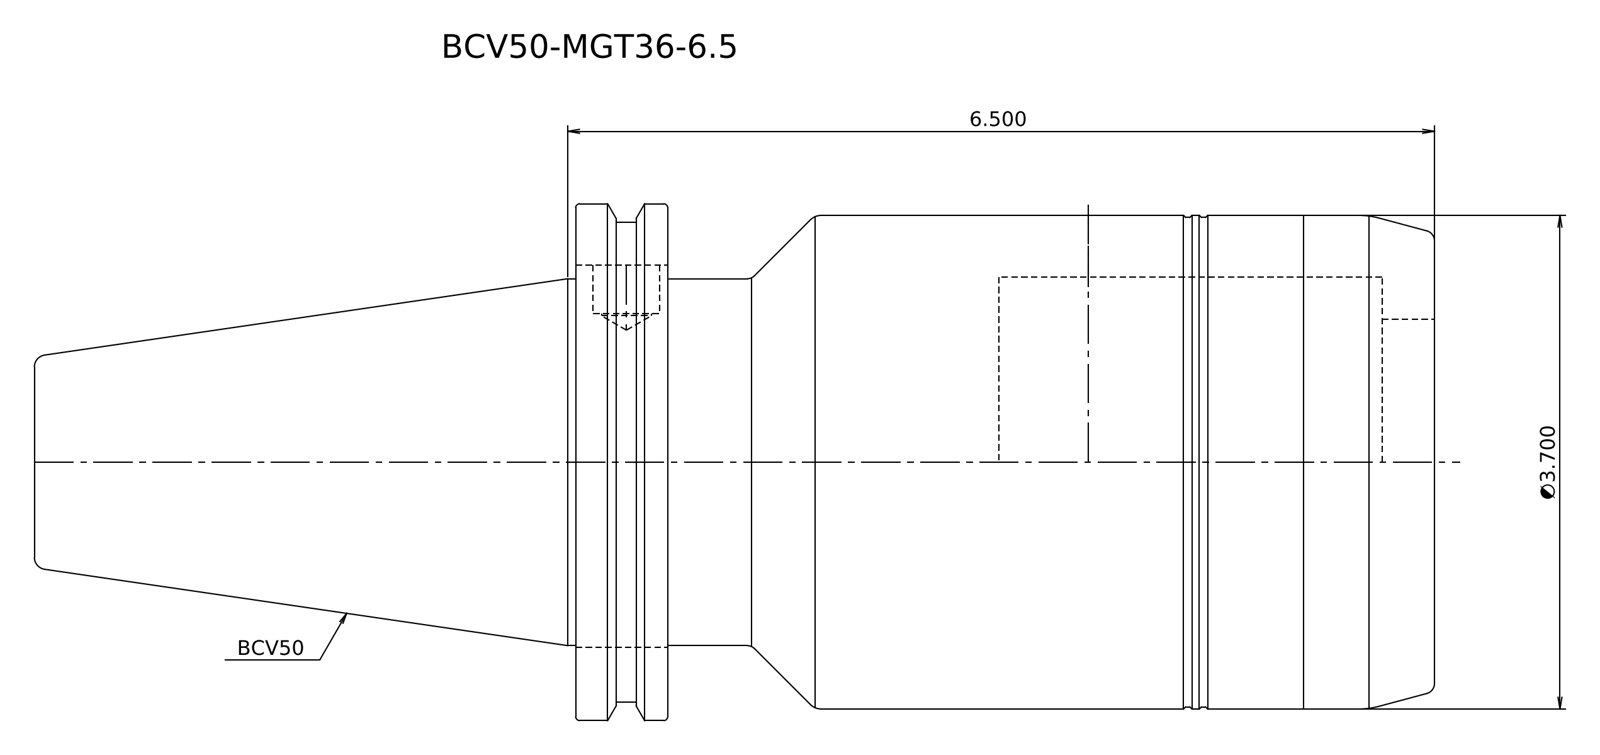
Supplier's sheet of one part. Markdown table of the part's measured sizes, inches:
| quantity | value |
| --- | --- |
| part name | BCV50-MGT36-6.5 |
| STEP written by | SolidWorks 2016 (CONFIG_CONTROL_DESIGN) |
| units | inches |
| bodies | 1 solid, 119 faces (38 planar, 29 cylindrical, 52 other) |
| overall size | 10.502 × 3.875 × 3.725 |
| volume | 78.23 in³ |
| surface area | 132.9 in² |
| round holes (diameter × count) | 0.374 × 1, 0.5 × 1, 0.874 × 1, 1.031 × 1 |
| round bosses / shafts (diameter × count) | 3.875 × 1, 3.701 × 1, 3.669 × 1, 3.594 × 1, 2.75 × 1, 2.726 × 1 |
| partial cylindrical surfaces (radius × count) | 0.03 × 12 |
| main face-to-face distances | 5.752, 0.691, 6.443, 0.679, 6.431, 4.059, 4.071, 4.75, 10.502, 2.875 |
| hole center spacings | 0.614 |
